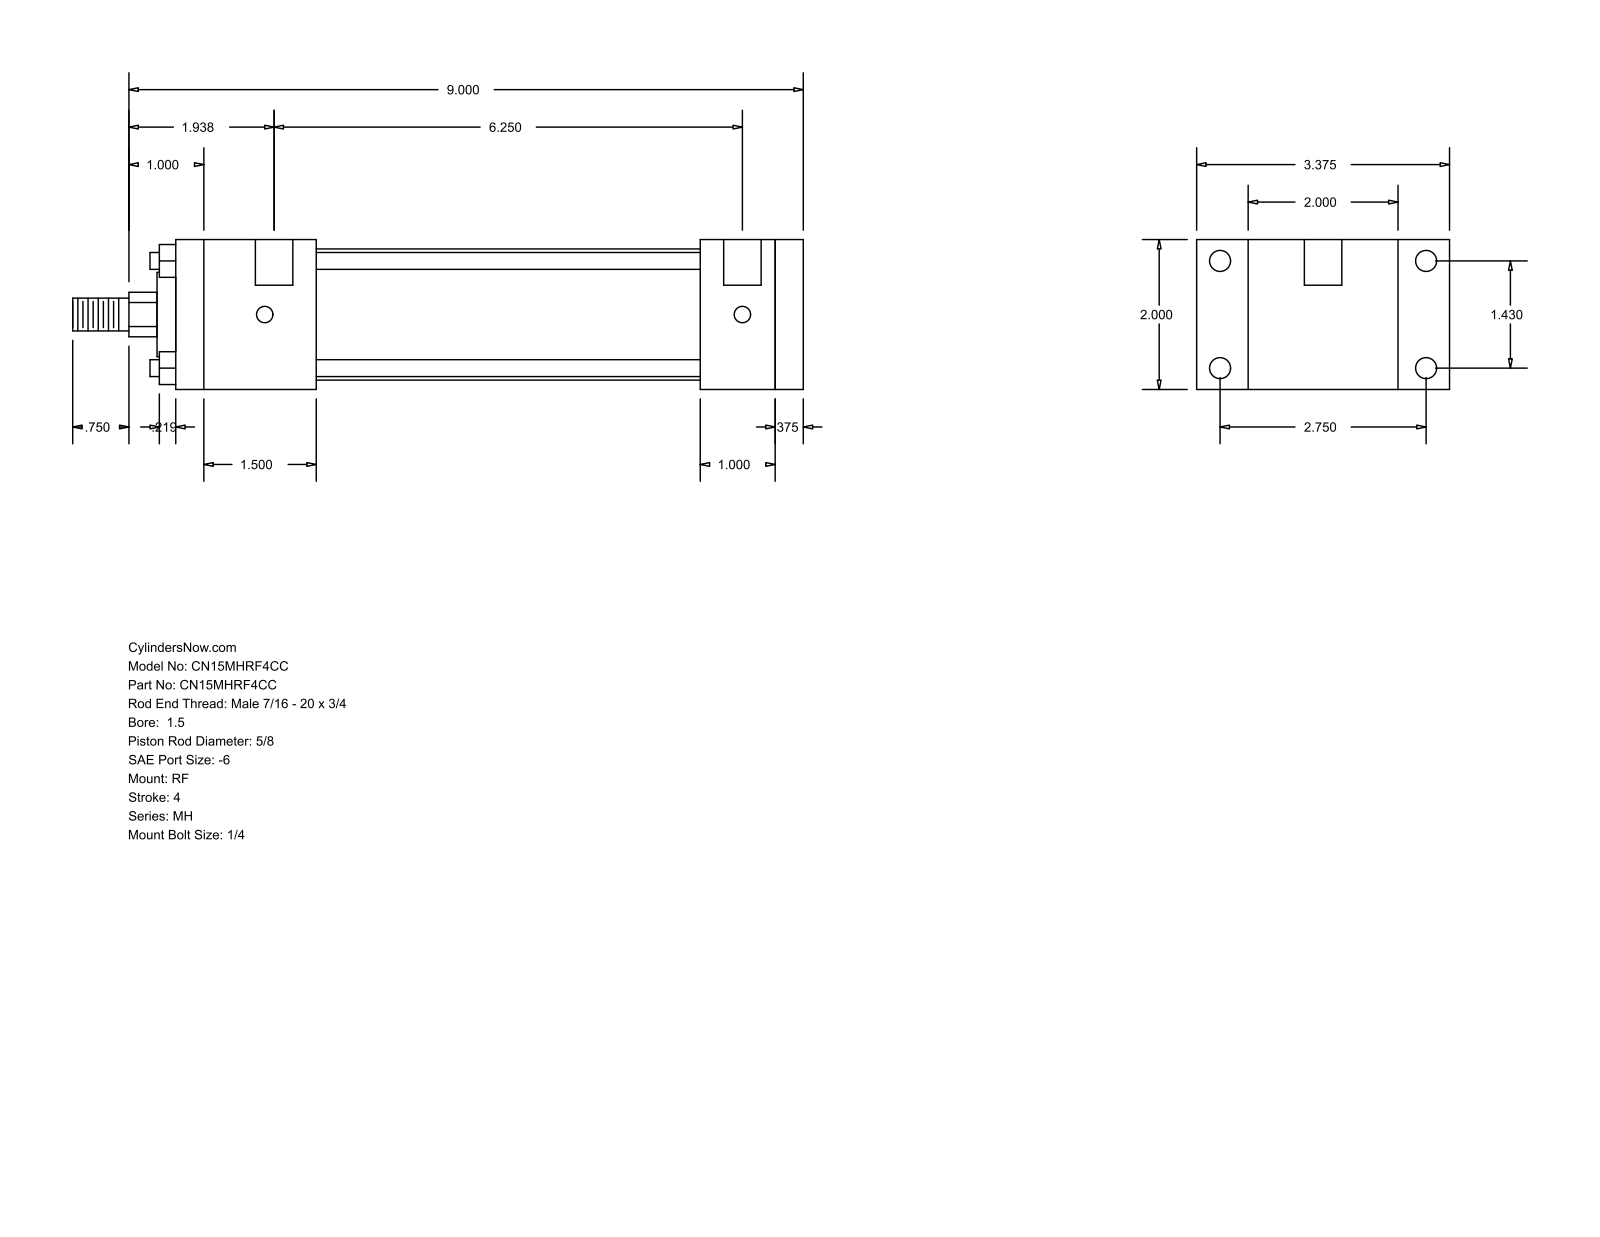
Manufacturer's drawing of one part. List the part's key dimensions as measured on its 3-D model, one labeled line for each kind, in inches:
Part name (STEP PRODUCT): MH_RF__0150_0.625
STEP written by: GSSL Pune (CONFIG_CONTROL_DESIGN)
Units: inches
Bodies: 0 solids, 92 faces (64 planar, 28 cylindrical, 0 other)
Overall size (bounding box): 9.75 × 3.375 × 2
Round holes (diameter × count): ⌀0.219 ×4, ⌀0.281 ×4, ⌀0.5 ×2
Round bosses / shafts (diameter × count): ⌀0.225 ×4, ⌀1.75 ×1, ⌀1.125 ×1, ⌀0.625 ×1, ⌀0.437 ×1
Partial cylindrical surfaces — rounded edges, fillets, slot ends (radius × count): R0.297 ×1
Main face-to-face distances: 2, 0.375, 8.375, 8, 0.687, 2.687, 7, 1, 1.375, 1.875
Hole centre spacings: 1.43, 2.75, 3.099, 6.375, 0.125, 6.25
